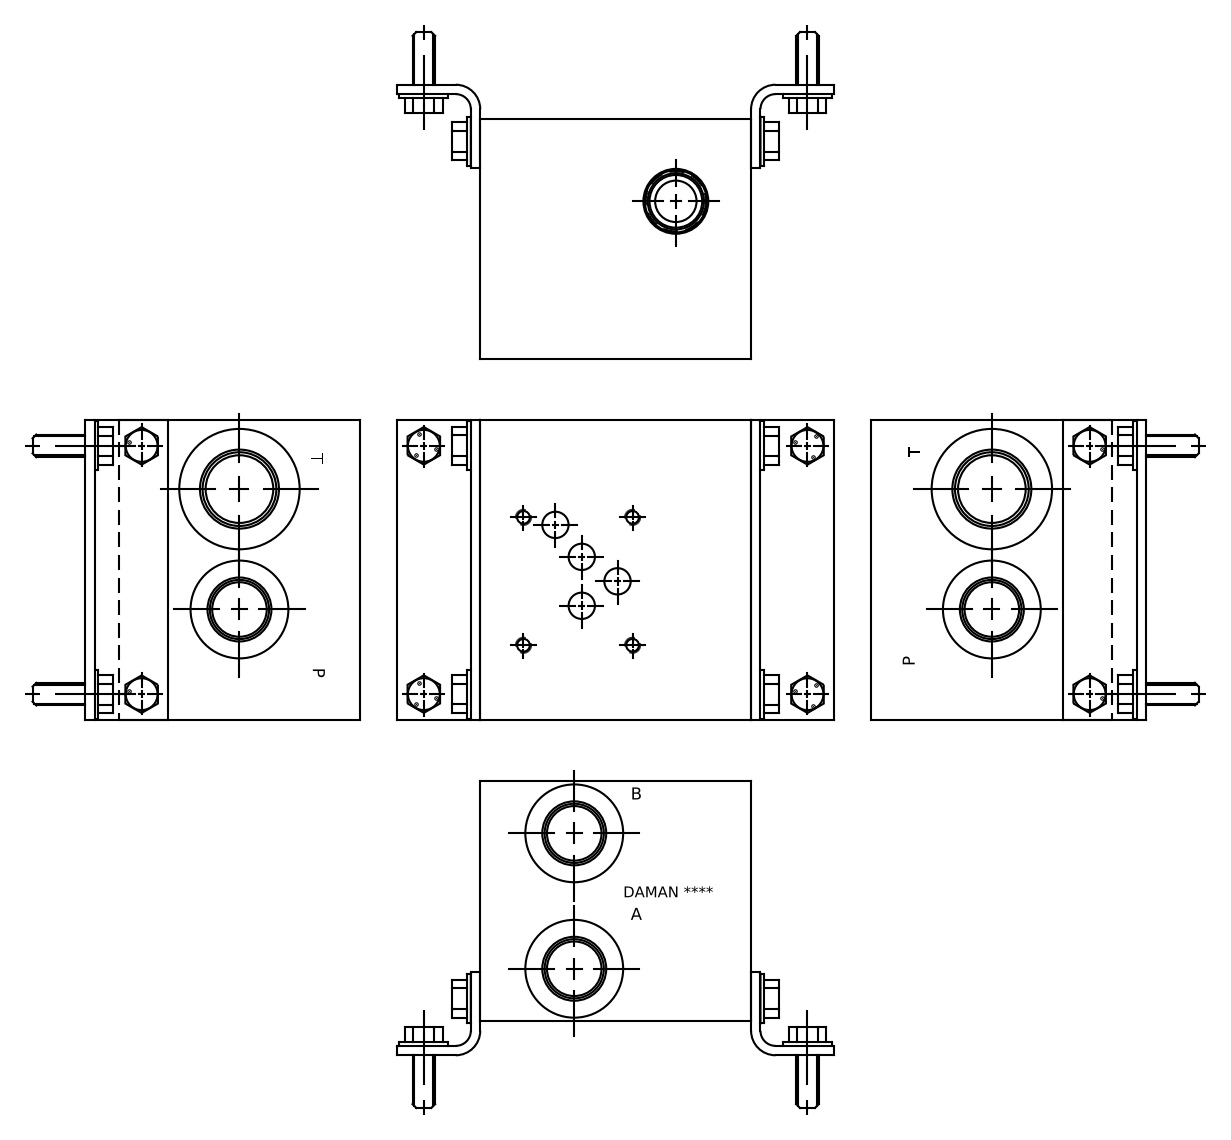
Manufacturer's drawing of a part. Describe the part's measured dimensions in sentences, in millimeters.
The part is named "Part_AD05HP013S~S_3D". Its 3-D file was written by "Autodesk Inventor 2019 (AUTOMOTIVE_DESIGN)". It is 1 solid with 569 faces: 326 planar, 58 cylindrical and 185 other. Overall it measures 127 by 114.3 by 101.6 millimeters. Its volume is 1 307 000 cubic millimeters and its surface area 104 066 square millimeters. Round holes: 4 of diameter 5.11, 4 of diameter 6.35, 3 of diameter 23.01, 3 of diameter 24.92, 3 of diameter 27.43, 3 of diameter 42.04, 2 of diameter 7.92, 2 of diameter 9.53, 2 of diameter 11.11, 2 of diameter 11.13, 2 of diameter 26.99, 2 of diameter 27. The main face-to-face distances are 101.6, 114.3, 127, 0.79, 113.51, 112.72, 126.21, 19.05, 19.84, 94.46. The hole center spacings are 18.28, 29.74, 46.05, 70.95, 13.88, 17.49, 20.63, 27.13.
